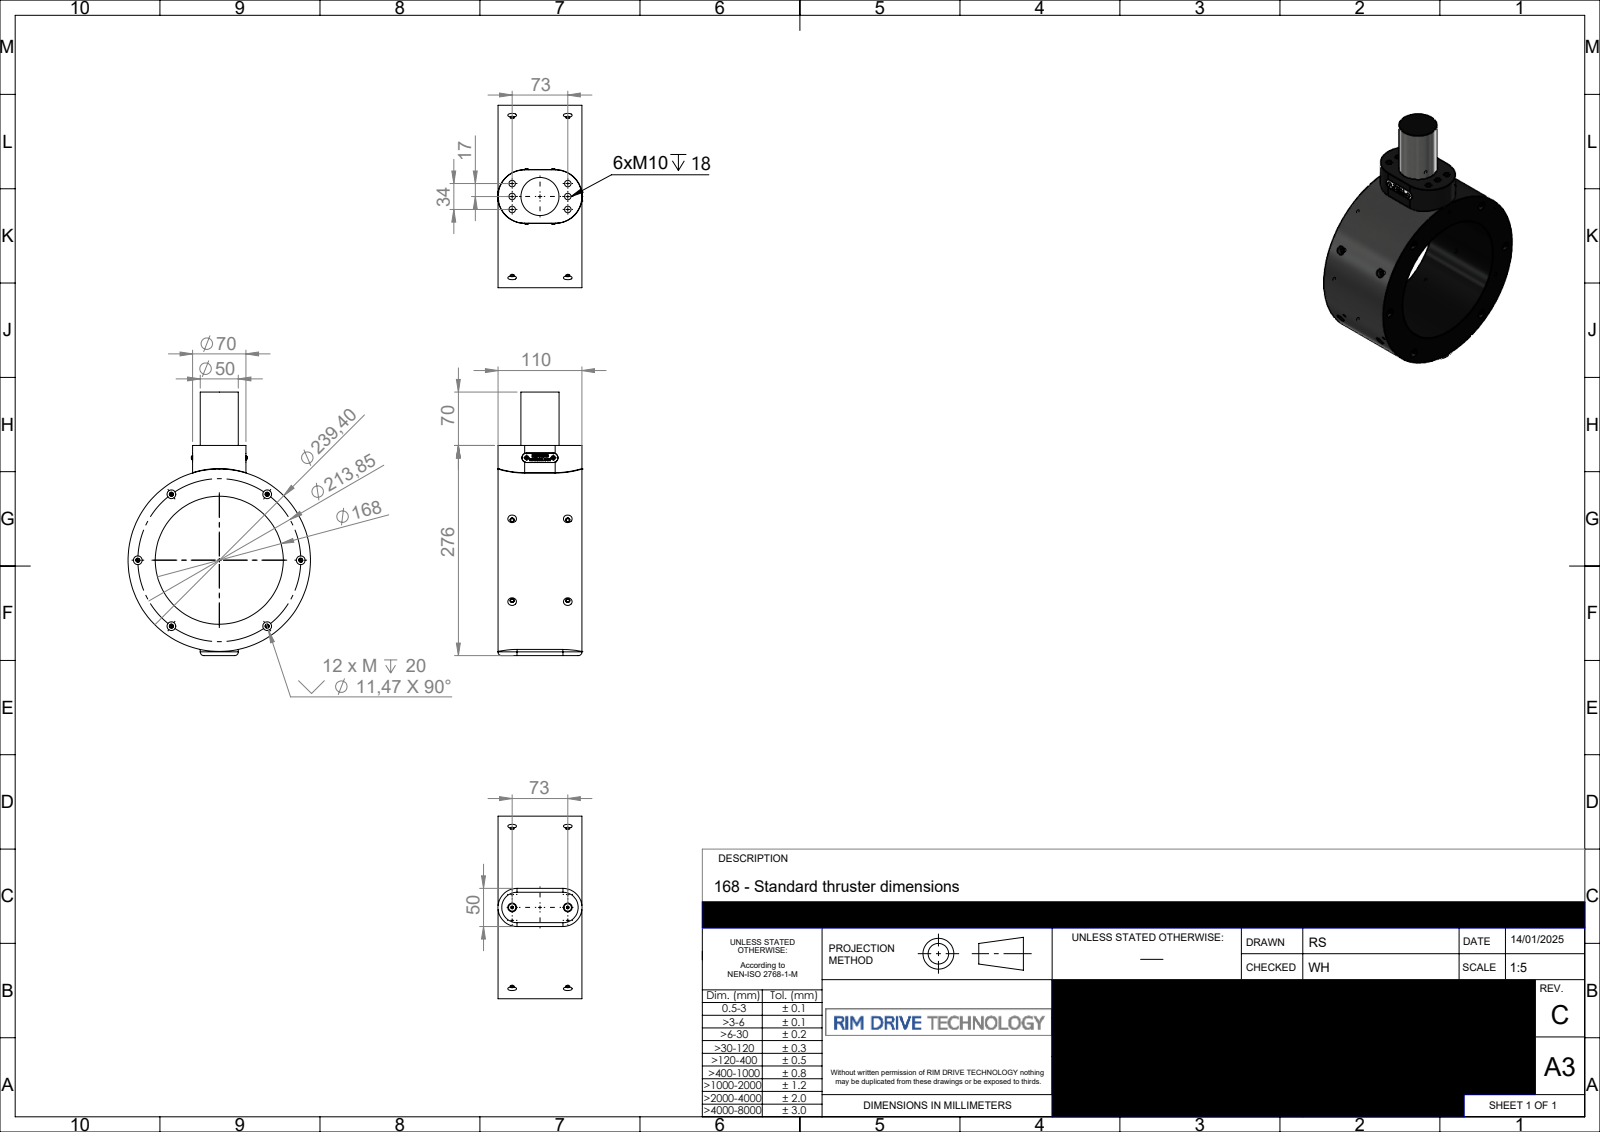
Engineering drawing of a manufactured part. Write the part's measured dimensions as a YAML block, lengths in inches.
part_name: "P-168-030-rev-C-ST"
step_written_by: "SolidWorks 2024 (AUTOMOTIVE_DESIGN)"
units: inches
bodies: {solids: 1, faces: 717, planar: 421, cylindrical: 88, other: 208}
overall_size: [13.616, 9.425, 4.345]
volume: 175.9
surface_area: 337.6
round_holes:
  - {diameter: 0.165, count: 12}
  - {diameter: 0.217, count: 6}
  - {diameter: 0.335, count: 6}
  - {diameter: 0.138, count: 2}
  - {diameter: 6.614, count: 1}
round_bosses_or_shafts:
  - {diameter: 0.217, count: 6}
  - {diameter: 0.38, count: 2}
  - {diameter: 0.224, count: 2}
  - {diameter: 0.118, count: 2}
  - {diameter: 9.425, count: 1}
  - {diameter: 1.969, count: 1}
partial_cylinders:
  - {radius: 0.02, count: 2}
  - {radius: 0.197, count: 2}
  - {radius: 0.242, count: 2}
  - {radius: 0.246, count: 2}
  - {radius: 0.984, count: 2}
  - {radius: 1.358, count: 2}
  - {radius: 1.378, count: 2}
face_to_face_distances: [4.333, 10.86, 2.756, 13.616, 0.394, 2.362, 10.055, 0.805, 3.561, 1.969]
hole_center_spacings: [2.874, 0.669, 2.951, 4.209, 7.502, 8.419, 1.339, 3.17]
